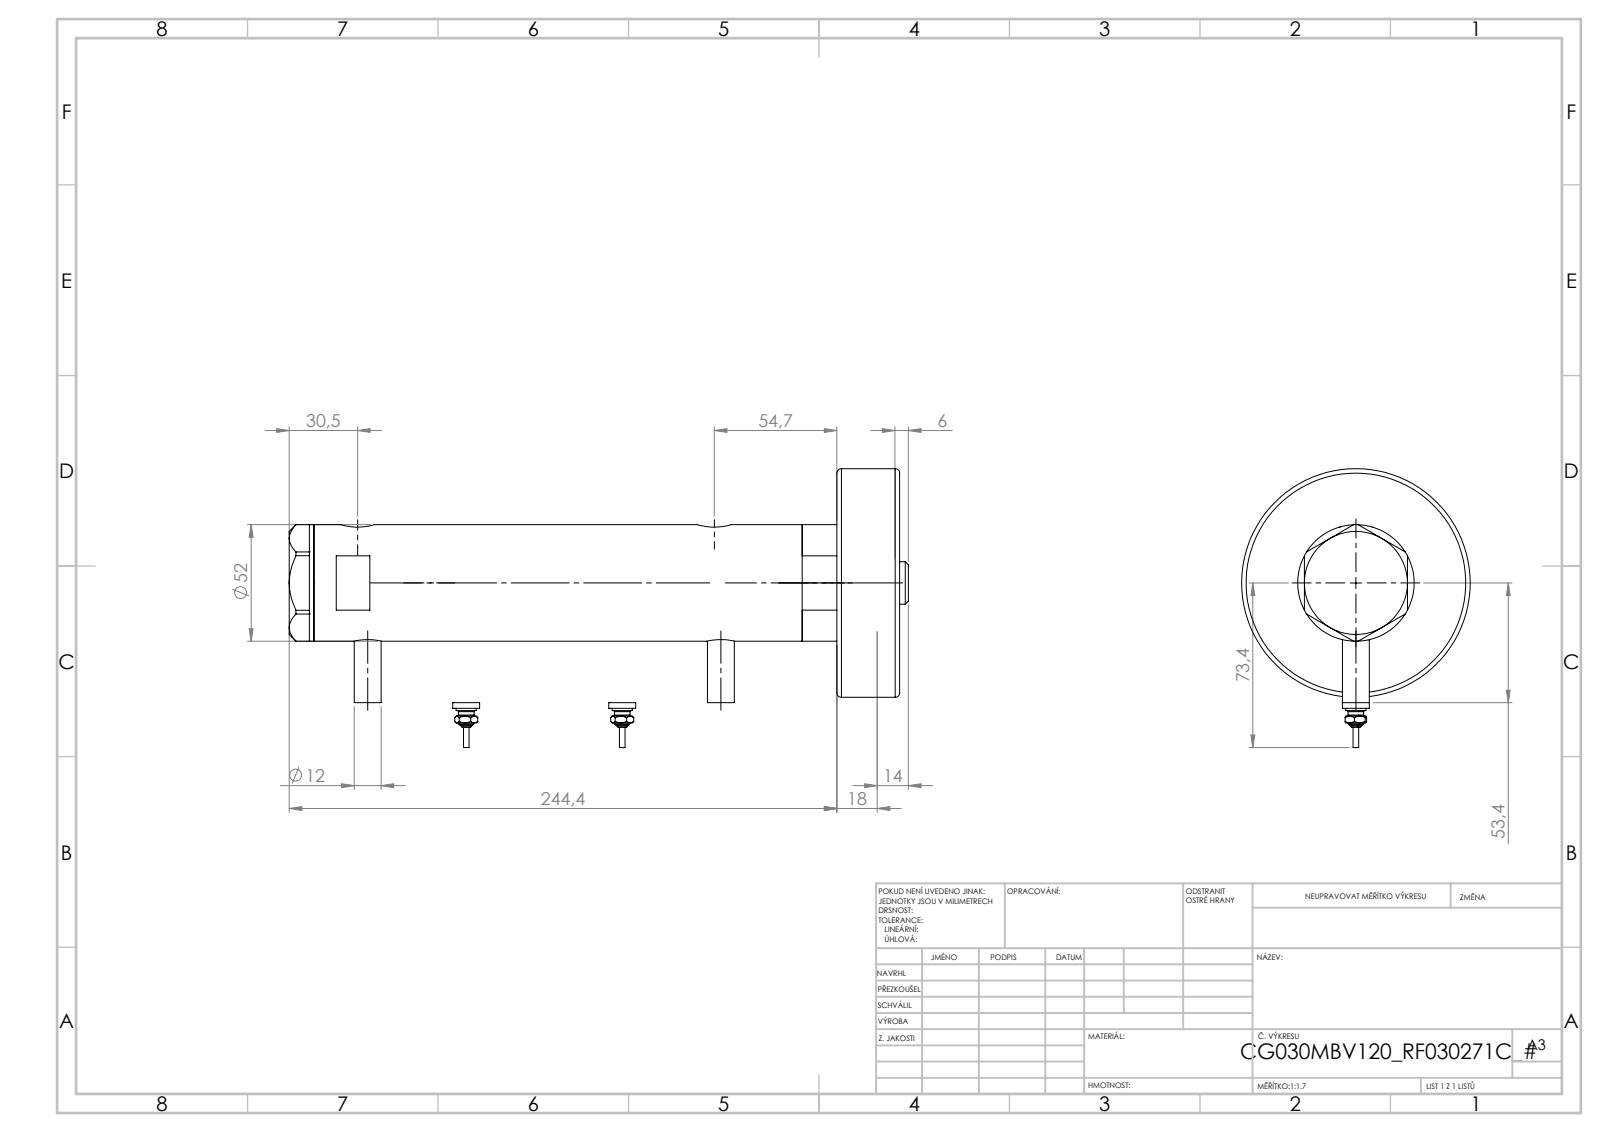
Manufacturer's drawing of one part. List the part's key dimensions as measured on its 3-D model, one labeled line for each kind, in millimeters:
Part name (STEP PRODUCT): V270CG_VC; V270CG_MIDDLE; V270CG_BACK; V270CG_SWITCH (+1 more)
STEP written by: SolidWorks 2019 (CONFIG_CONTROL_DESIGN)
Units: millimetres
Bodies: 6 solids, 246 faces (95 planar, 77 cylindrical, 74 other)
Overall size (bounding box): 269.02 × 84.3 × 52
Volume: 478 097 mm³ · Surface area: 105 489 mm²
Round holes (diameter × count): ⌀5 ×2, ⌀9.73 ×2, ⌀12.5 ×2, ⌀15 ×2, ⌀6.5 ×1, ⌀20 ×1, ⌀21.5 ×1, ⌀30 ×1, ⌀33 ×1, ⌀44 ×1
Round bosses / shafts (diameter × count): ⌀12 ×3, ⌀9 ×2, ⌀7 ×2, ⌀4.34 ×2, ⌀2.4 ×2, ⌀52 ×1, ⌀40 ×1, ⌀38 ×1
Main face-to-face distances: 23.8, 11, 34.8, 46, 184.54, 173.54, 149.74, 220.94, 209.94, 186.14
Hole centre spacings: 2.9, 4.5, 146.75, 149.65, 151.25, 154.15, 2.89, 2.91
